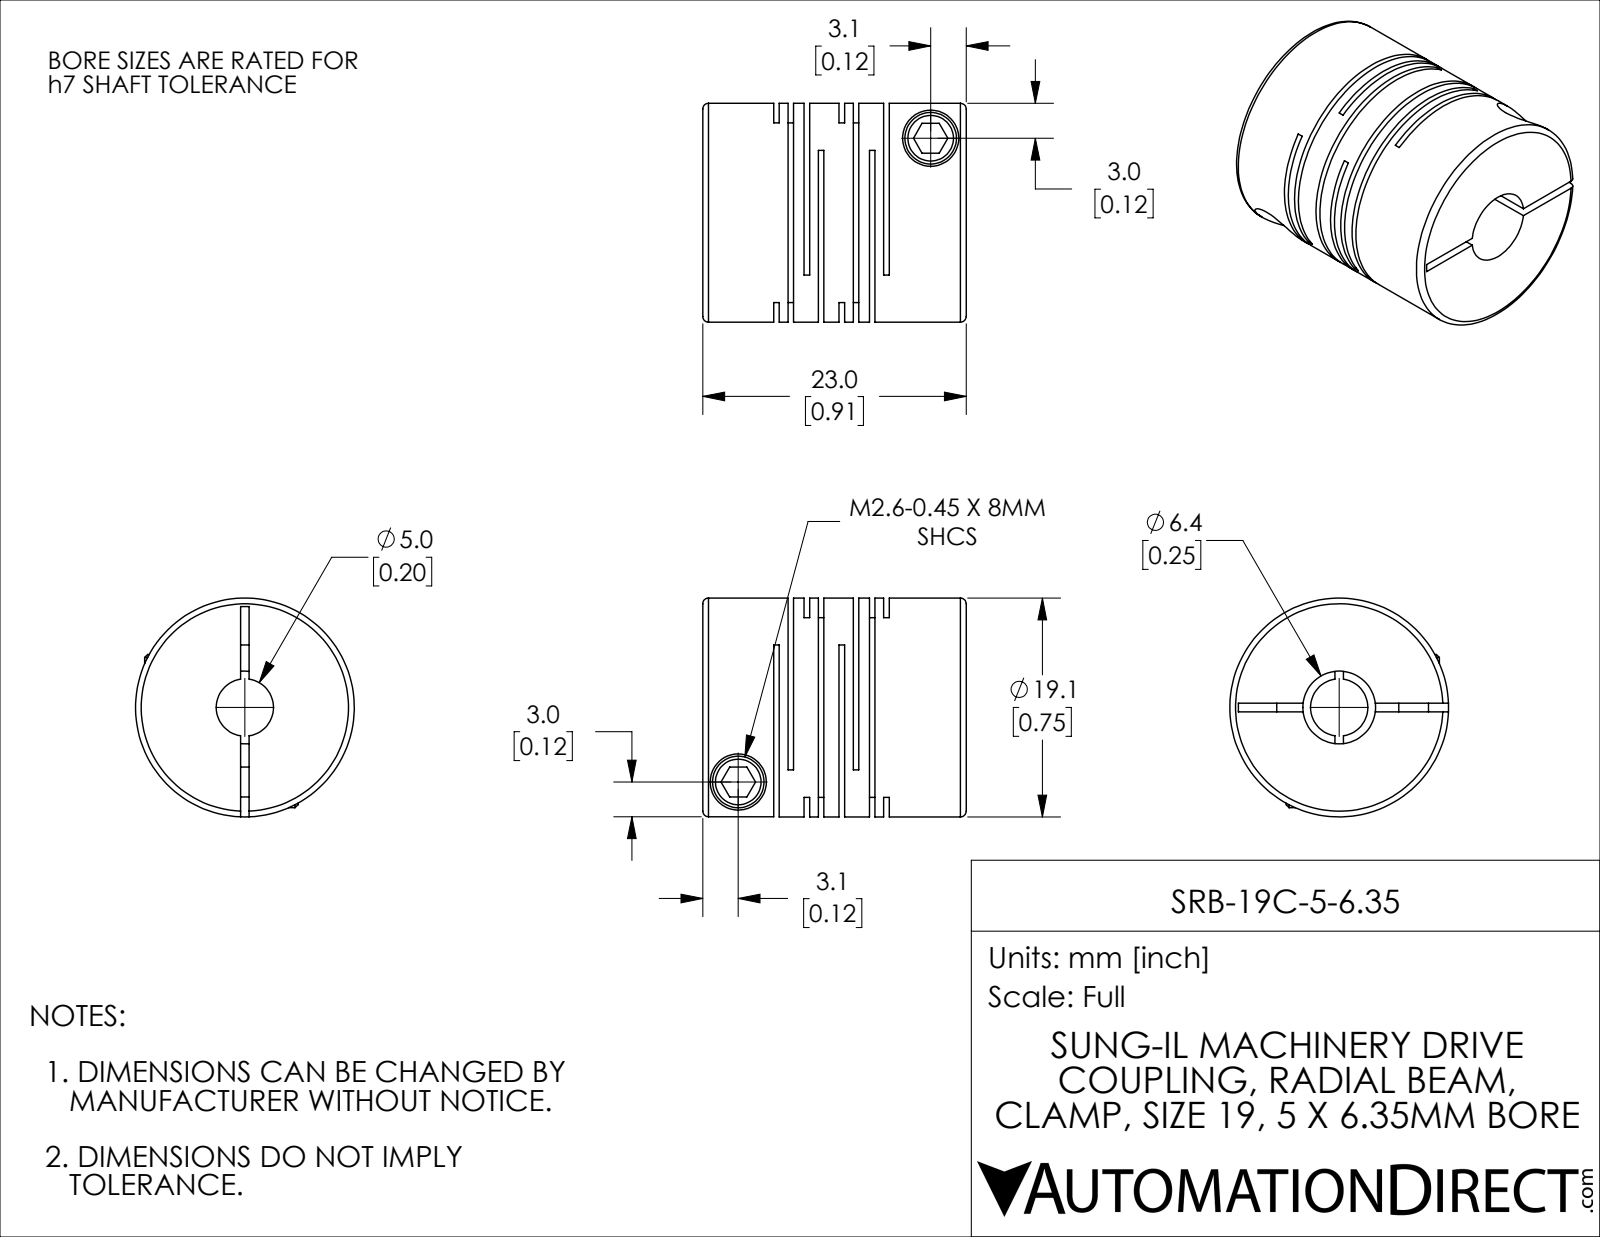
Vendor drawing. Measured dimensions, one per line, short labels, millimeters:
name: SRB-19C-5-6.35
written by: SolidWorks 2021 (CONFIG_CONTROL_DESIGN)
unit: mm
bodies: 1 solid, 114 faces (60 planar, 42 cylindrical, 12 other)
size: 23 × 19.1 × 19.1
volume: 4 887 mm³; area: 5 979 mm²
holes: 2× ⌀2.6, 2× ⌀4.9, 1× ⌀5, 1× ⌀6.35
bosses: 2× ⌀4.5, 1× ⌀19.1
face distances: 0.48, 2.65, 1.25, 5.7, 2.17, 3.05, 4.45, 5.22, 0.77, 1.4
